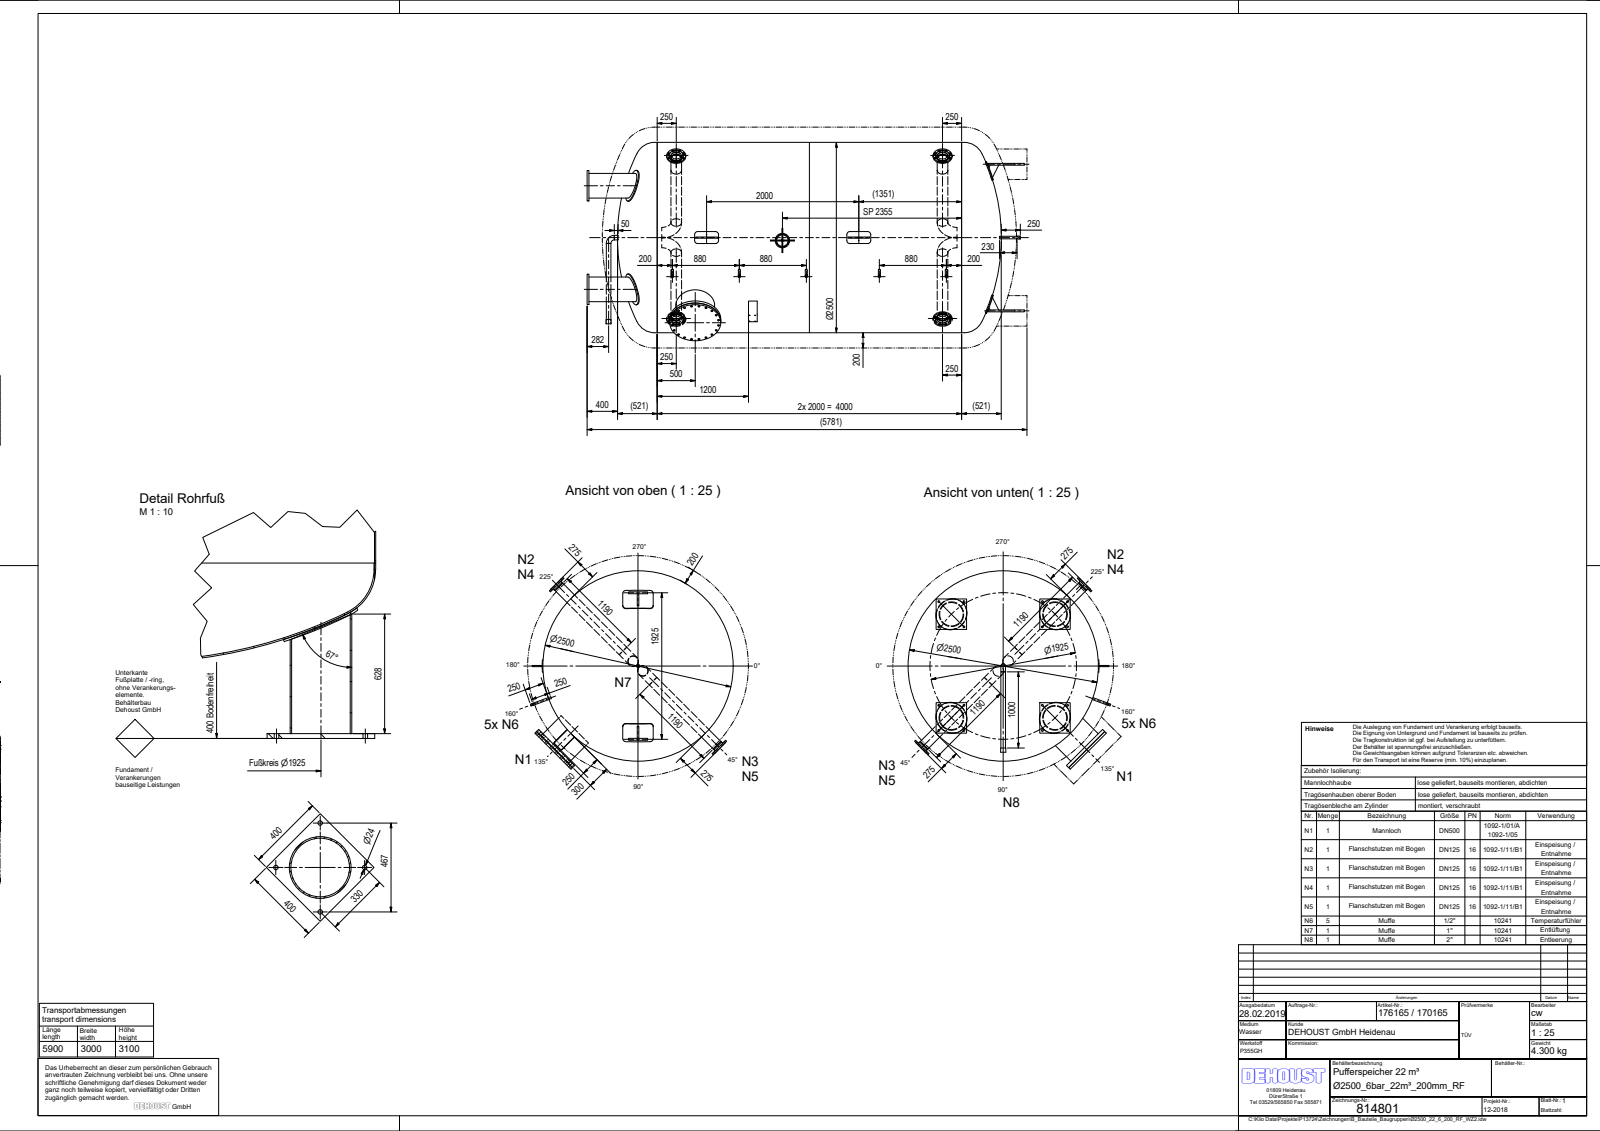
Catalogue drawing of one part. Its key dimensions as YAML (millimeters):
part_name: "Ø2500_22_6_200_RF_WZ2; Klöpper_Gew_Ø2500_8,3; Zyl_Ø2500_6x4000_2019; TÖB_Puffer_Ø2500_8, 3_200 (+8 more)"
step_written_by: "Autodesk Inventor 2019 (AUTOMOTIVE_DESIGN)"
units: millimeters
bodies: {solids: 58, faces: 453, planar: 178, cylindrical: 225, other: 50}
overall_size: [5745.05, 2664.05, 2604.82]
volume: 479700000
surface_area: 106800000
round_holes:
  - {diameter: 26, count: 40}
  - {diameter: 18, count: 32}
  - {diameter: 24, count: 16}
  - {diameter: 131.7, count: 8}
  - {diameter: 18.63, count: 5}
  - {diameter: 21.7, count: 5}
  - {diameter: 26.9, count: 5}
  - {diameter: 5.8, count: 4}
  - {diameter: 139.7, count: 4}
  - {diameter: 307.9, count: 4}
  - {diameter: 5, count: 2}
  - {diameter: 52.3, count: 2}
round_bosses_or_shafts:
  - {diameter: 139.7, count: 8}
  - {diameter: 26.9, count: 5}
  - {diameter: 26.4, count: 5}
  - {diameter: 420, count: 4}
  - {diameter: 323.9, count: 4}
  - {diameter: 250, count: 4}
  - {diameter: 188, count: 4}
  - {diameter: 670, count: 2}
partial_cylinders:
  - {radius: 42, count: 16}
  - {radius: 6, count: 8}
  - {radius: 5, count: 2}
  - {radius: 10, count: 2}
  - {radius: 36, count: 2}
  - {radius: 72, count: 2}
  - {radius: 125, count: 1}
  - {radius: 1259, count: 1}
face_to_face_distances: [25, 2778.97, 3063.97, 2753.97, 3038.97, 285, 600, 27.99, 1857.5, 2142.5]
hole_center_spacings: [310, 105, 191.59, 3500, 501.59, 194.02, 880, 552.42]
